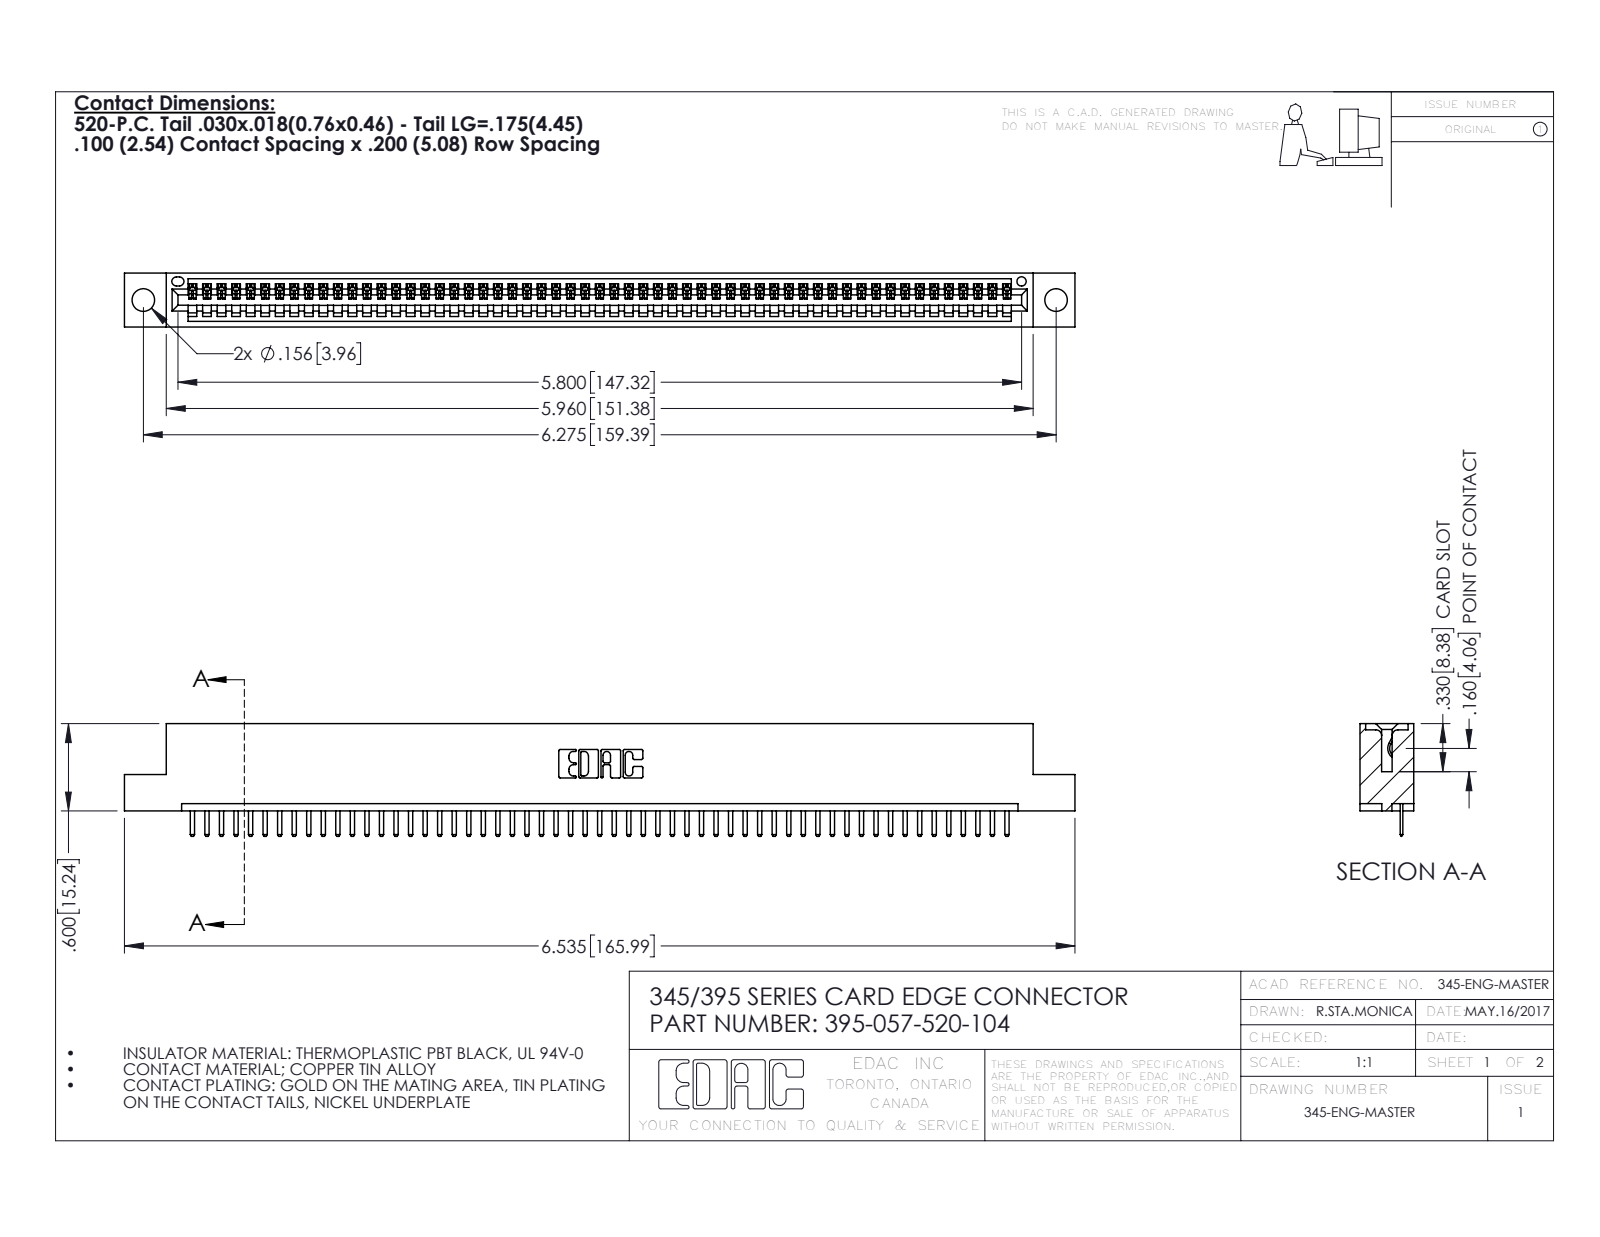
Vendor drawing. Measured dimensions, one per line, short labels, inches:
name: 395-057-520-104; 345 Part_Flush Mounting Lugs - 0.156 Dia-TH; 345-292-001_345-293-120
written by: SolidWorks 2016 (CONFIG_CONTROL_DESIGN)
unit: in
bodies: 58 solids, 3660 faces (2474 planar, 1186 cylindrical, 0 other)
size: 6.535 × 0.775 × 0.37
volume: 0.954 in³; area: 31.4 in²
holes: 2× ⌀0.156, 1× ⌀0.064
rounds: 116× R0.01, 114× R0.006, 22× R0.01, 6× R0.007, 6× R0.031, 3× R0.026, 2× R0.031, 2× R0.04
face distances: 0.298, 0.072, 0.37, 0.2, 0.098, 0.272, 0.025, 0.225, 0.072, 0.149
hole spacings: 0.27, 6.039, 6.275
